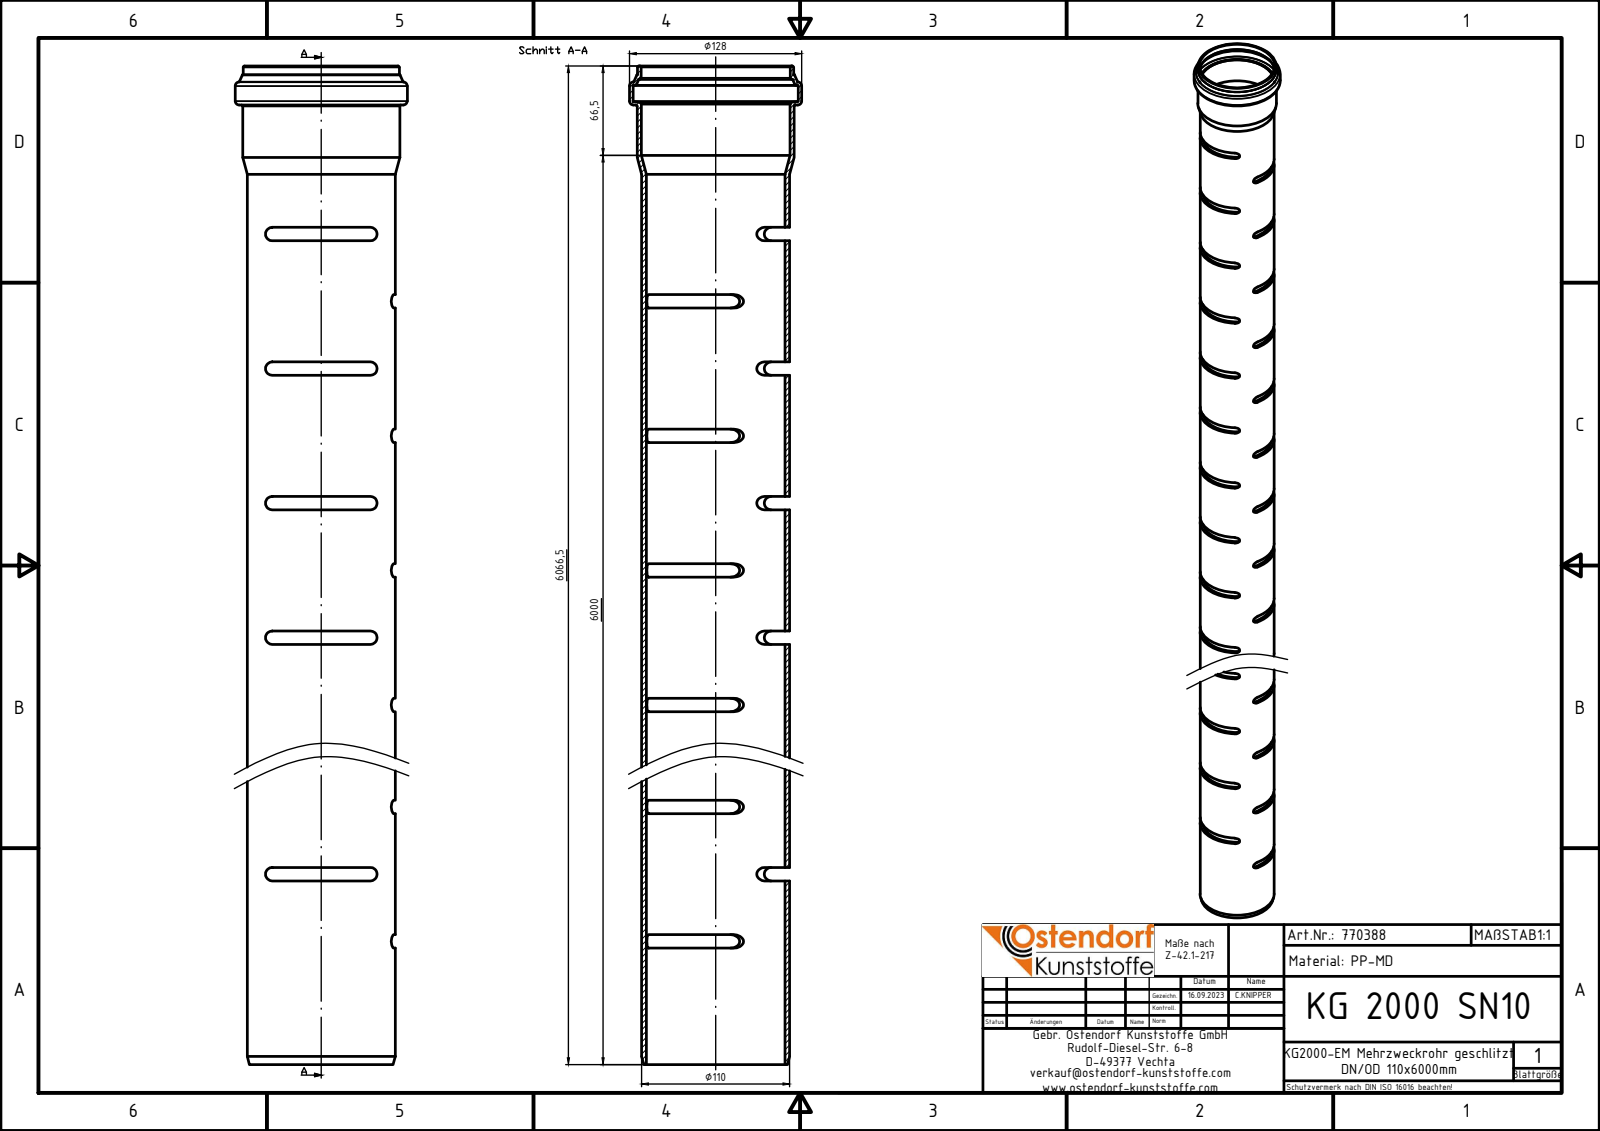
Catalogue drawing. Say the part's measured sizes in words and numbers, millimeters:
The part is named "770388z". Its 3-D file was written by "Autodesk Inventor 2024 (AUTOMOTIVE_DESIGN)". It is 1 solid with 508 faces: 241 planar, 245 cylindrical and 22 other. Overall it measures 6066.5 by 128 by 128 millimeters. Its volume is 6 760 000 cubic millimeters and its surface area 3 940 000 square millimeters. Round holes: 1 of diameter 102.96, 1 of diameter 110.5, 1 of diameter 110.9, 1 of diameter 122.8. Round bosses or shafts: 1 of diameter 128, 1 of diameter 116.7, 1 of diameter 116.1, 1 of diameter 110. Partial cylindrical surfaces (rounded edges, fillets, slot ends): 236 of radius 5. The main face-to-face distances are 100, 200, 300, 400, 500, 600, 700, 800, 900, 1000.
